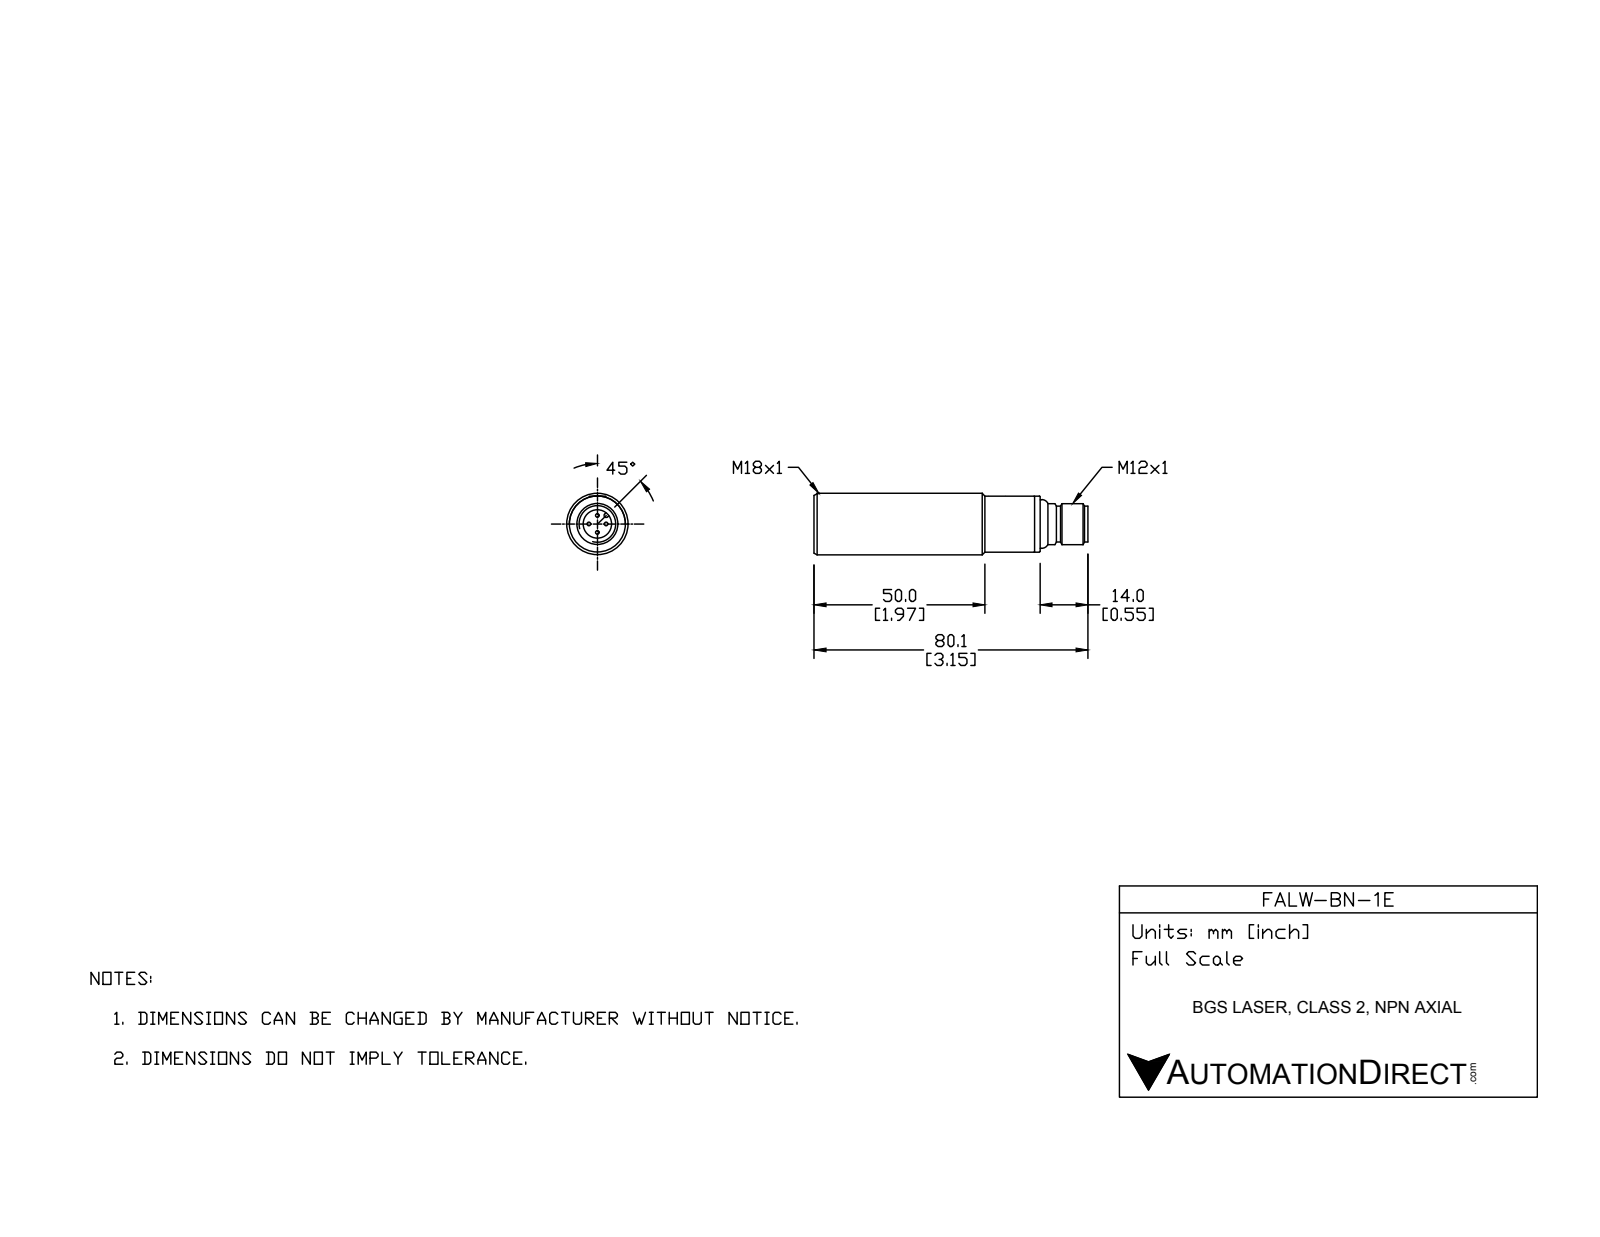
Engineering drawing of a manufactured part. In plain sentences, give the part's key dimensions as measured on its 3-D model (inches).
The part is named "FALW-BN-1E". Its 3-D file was written by "SolidWorks 2017 (AUTOMOTIVE_DESIGN)". It is 10 solids with 166 faces: 50 planar, 73 cylindrical and 43 other. Overall it measures 3.154 by 0.709 by 0.709 inches. Its volume is 1.039 cubic inches and its surface area 10.09 square inches. Round holes: 4 of diameter 0.039, 4 of diameter 0.043, 1 of diameter 0.106, 1 of diameter 0.185, 1 of diameter 0.278, 1 of diameter 0.327, 1 of diameter 0.622. Round bosses or shafts: 1 of diameter 0.709, 1 of diameter 0.646, 1 of diameter 0.559, 1 of diameter 0.472, 1 of diameter 0.413, 1 of diameter 0.276, 1 of diameter 0.189. Partial cylindrical surfaces (rounded edges, fillets, slot ends): 4 of radius 0.02, 1 of radius 0.024, 1 of radius 0.331. The main face-to-face distances are 0.063, 2.531, 0.055, 2.476, 2.469, 2.539, 2.594, 2.795, 2.74, 2.732. The hole center spacings are 0.098, 0.139, 0.197.
